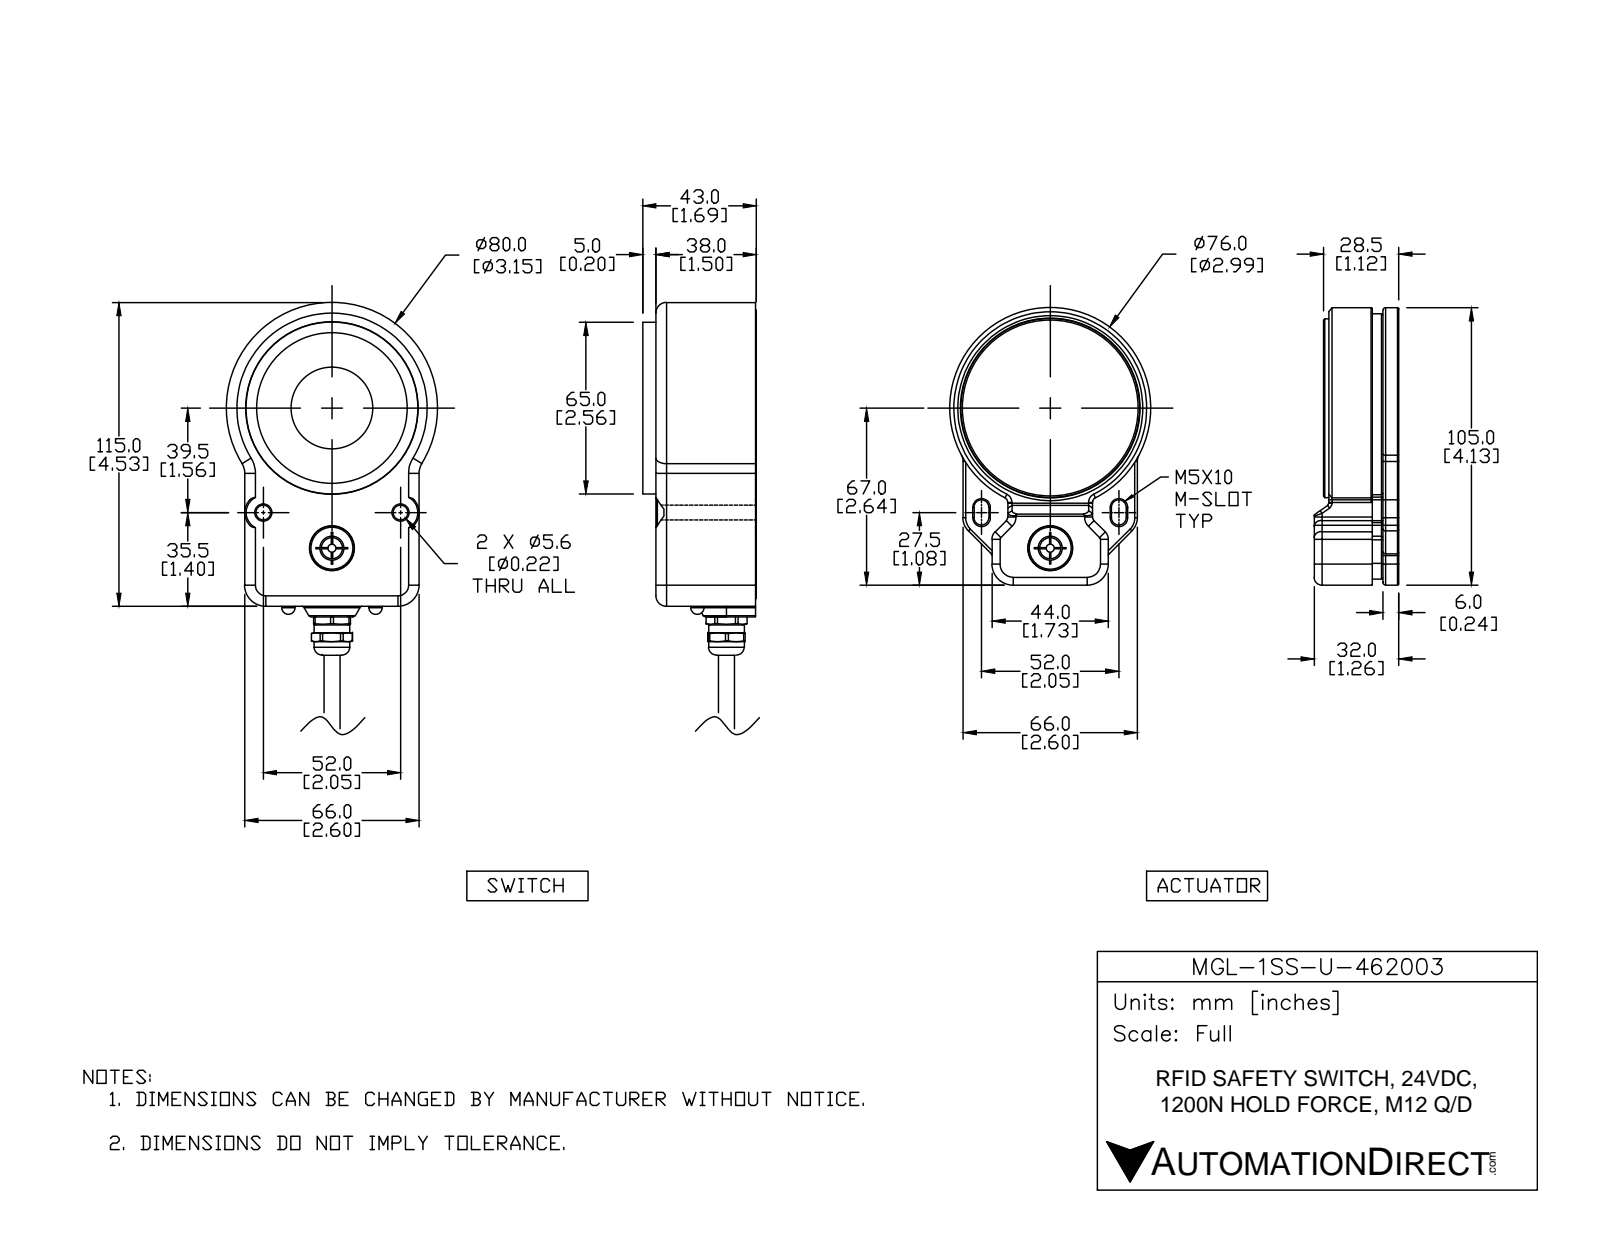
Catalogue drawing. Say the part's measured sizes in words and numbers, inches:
The part is named "MGL-1SS-U-462003; MGL-1SS-U-462003_2; MGL-1SS-U-462003_1". Its 3-D file was written by "SolidWorks 2017 (AUTOMOTIVE_DESIGN)". It is 19 solids with 1647 faces: 423 planar, 679 cylindrical and 545 other. Overall it measures 8.465 by 3.15 by 2.854 inches. Its volume is 19.52 cubic inches and its surface area 219.9 square inches. Round holes: 8 of diameter 0.098, 6 of diameter 0.13, 6 of diameter 0.197, 5 of diameter 0.453, 3 of diameter 0.157, 3 of diameter 0.315, 3 of diameter 0.354, 2 of diameter 0.22, 2 of diameter 0.276, 1 of diameter 0.252, 1 of diameter 0.266, 1 of diameter 0.268. Round bosses or shafts: 4 of diameter 0.02, 2 of diameter 0.472, 2 of diameter 0.228, 2 of diameter 0.22, 2 of diameter 0.118, 2 of diameter 0.047, 1 of diameter 2.992, 1 of diameter 2.811. Partial cylindrical surfaces (rounded edges, fillets, slot ends): 188 of radius 0.02, 64 of radius 0.039, 26 of radius 0.079, 17 of radius 0.012, 13 of radius 0.118, 12 of radius 0.157, 10 of radius 0.217, 7 of radius 0.024. The main face-to-face distances are 0.236, 0.315, 0.098, 0.413, 1.378, 2.303, 1.122, 0.118, 0.354, 2.205. The hole center spacings are 1.392, 1.969, 0.984, 1.28, 1.537, 0.787, 1.364, 0.349.
